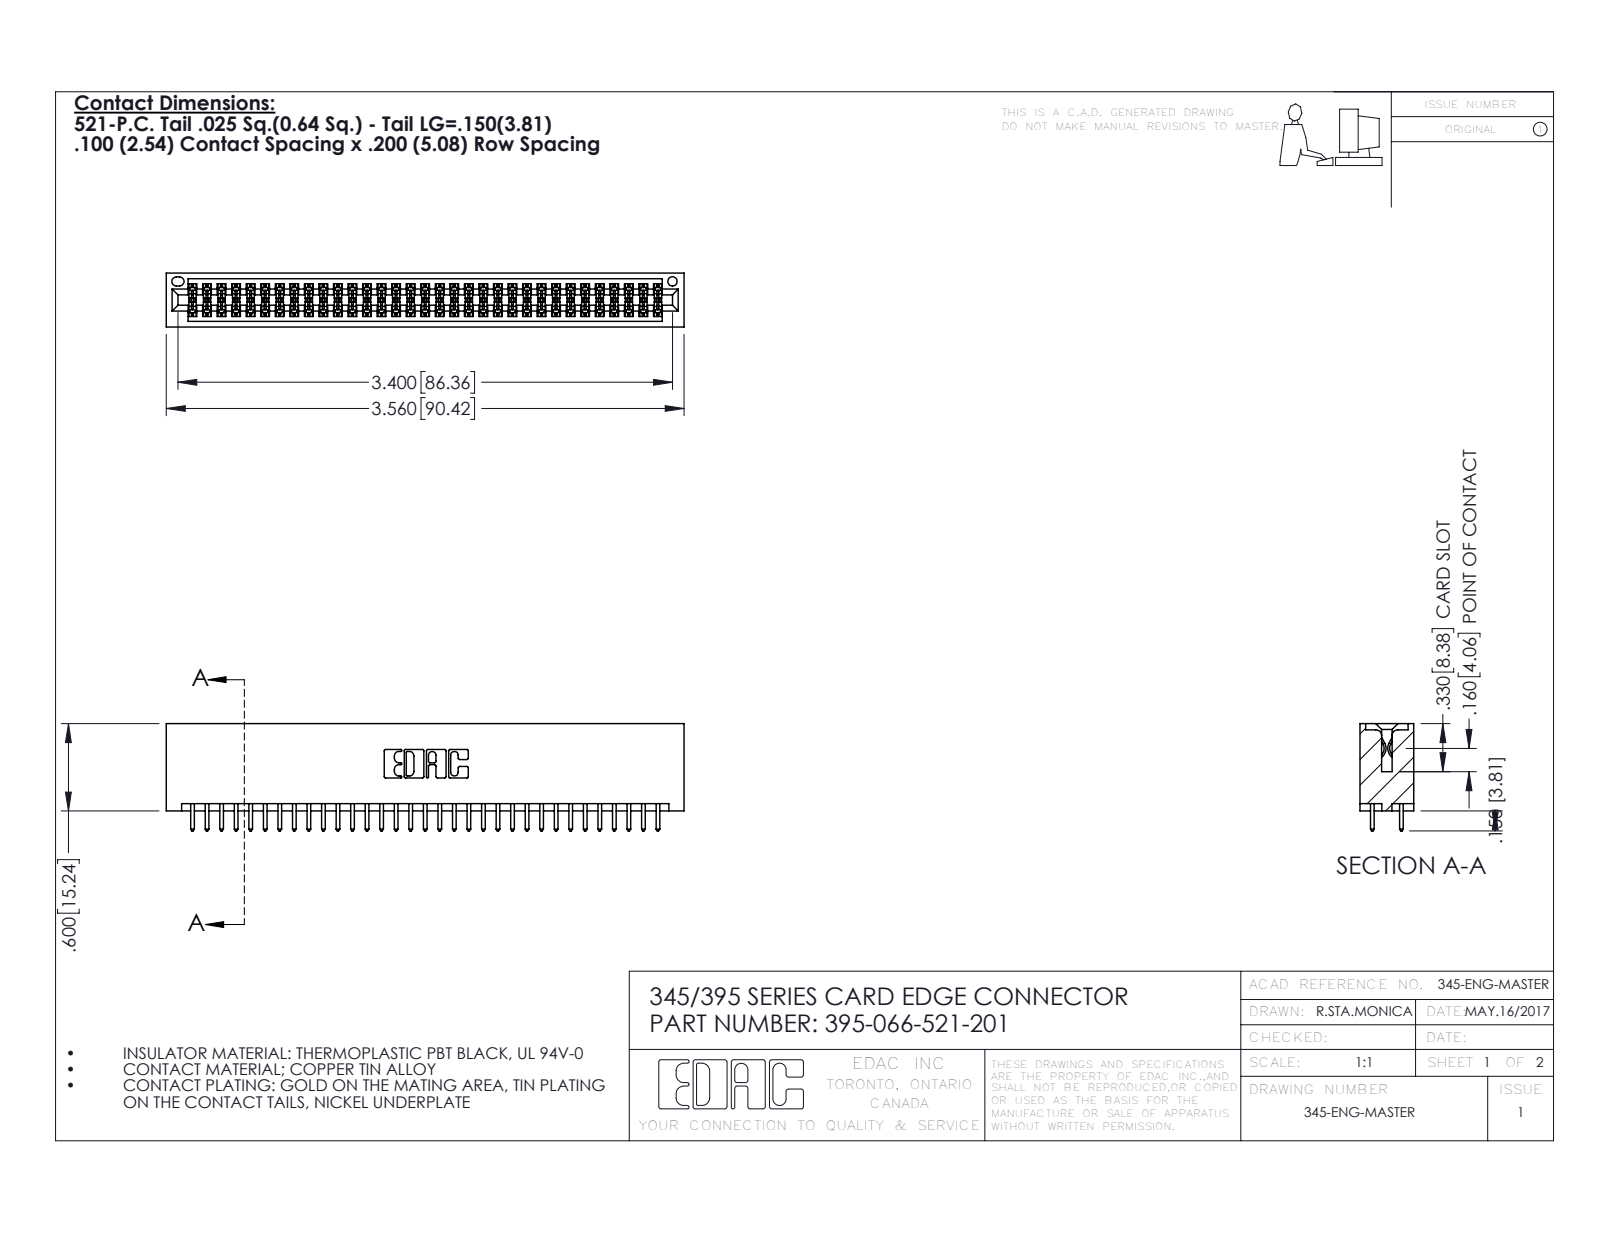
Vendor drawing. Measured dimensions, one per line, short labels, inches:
name: 345-292-001_345-293-121; 345 Part_No Mounting Lugs; 395-066-521-201
written by: SolidWorks 2016 (CONFIG_CONTROL_DESIGN)
unit: in
bodies: 67 solids, 3418 faces (2254 planar, 1164 cylindrical, 0 other)
size: 3.56 × 0.737 × 0.37
volume: 0.567 in³; area: 21.21 in²
holes: 1× ⌀0.064
rounds: 99× R0.006, 66× R0.01, 22× R0.01, 6× R0.007, 6× R0.031, 3× R0.026, 2× R0.014, 2× R0.019
face distances: 0.298, 0.072, 0.2, 0.098, 0.272, 0.025, 0.37, 0.225, 0.175, 0.149
